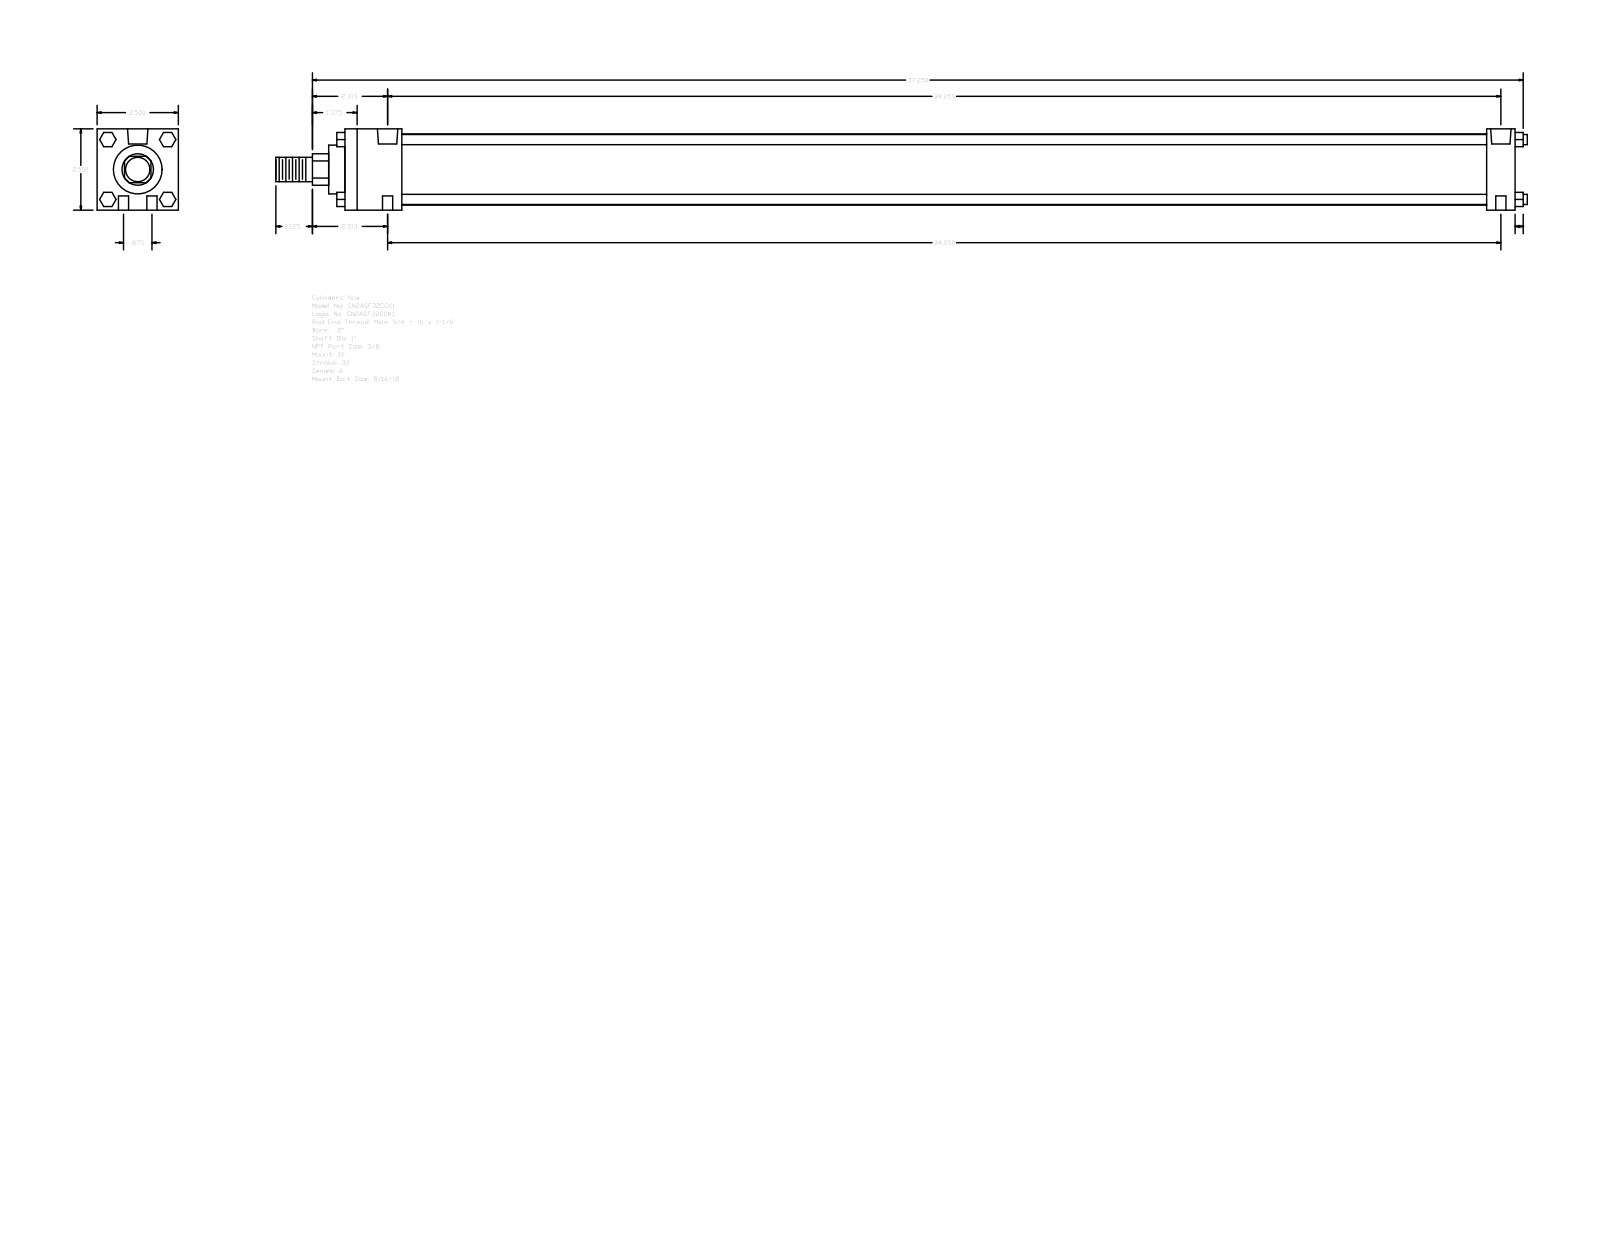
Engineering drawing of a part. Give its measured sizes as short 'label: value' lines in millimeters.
name: A_SF__0200_1
written by: GSSL Pune (CONFIG_CONTROL_DESIGN)
unit: mm
bodies: 0 solids, 124 faces (94 planar, 30 cylindrical, 0 other)
size: 977.9 × 63.5 × 63.5
holes: 4× ⌀7.94, 2× ⌀5.56, 2× ⌀15.93
bosses: 4× ⌀7.94, 1× ⌀55.63, 1× ⌀38.1, 1× ⌀25.4, 1× ⌀19.05
rounds: 1× R12.29
face distances: 63.5, 914.4, 892.18, 22.22, 44.45, 847.73, 869.95, 12.7, 927.1, 6.35
hole spacings: 11.11, 870.02, 869.95, 22.22, 870.23, 864.38
